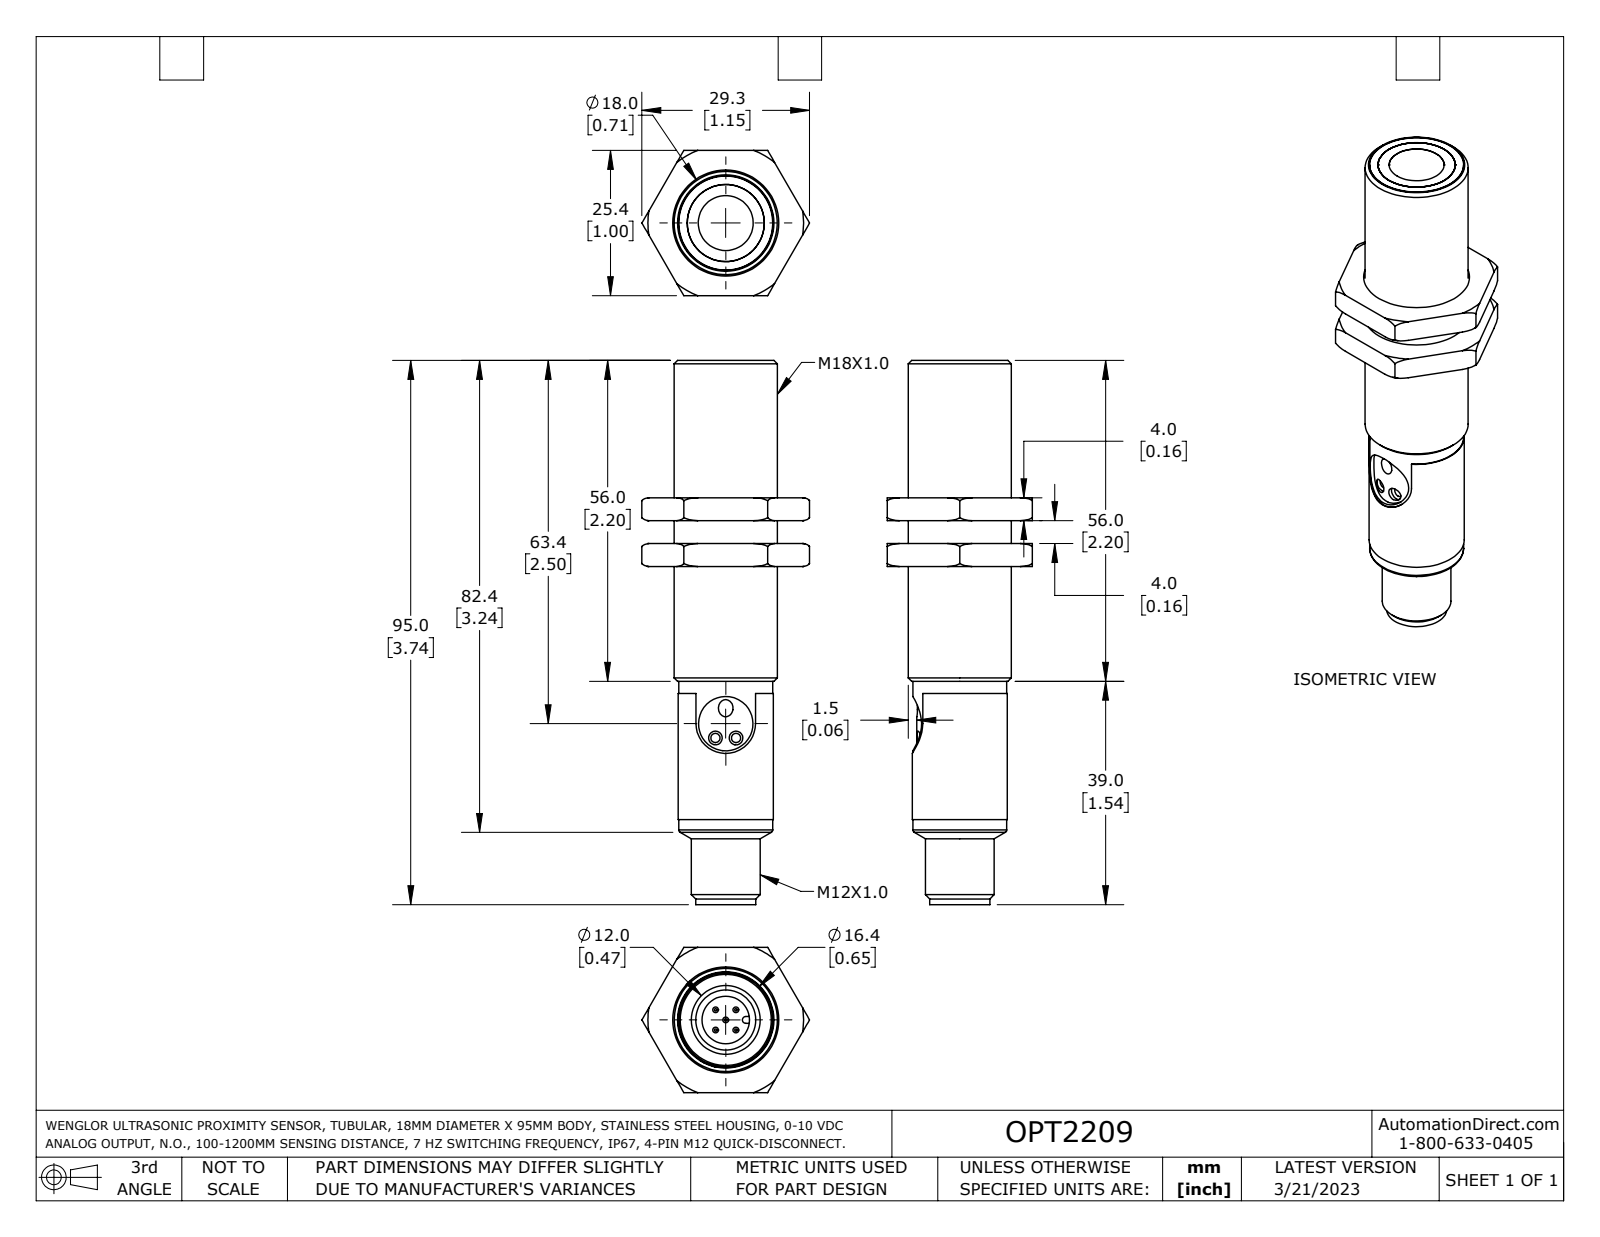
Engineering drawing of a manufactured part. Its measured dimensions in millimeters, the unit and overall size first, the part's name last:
Units: millimetres
Overall size (bounding box): 95 × 29.3 × 25.3
Round holes (diameter × count): ⌀2.4 ×2, ⌀3.8 ×1, ⌀4.5 ×1, ⌀8.3 ×1, ⌀9.5 ×1, ⌀9.6 ×1, ⌀13.5 ×1, ⌀17.5 ×1
Round bosses / shafts (diameter × count): ⌀1 ×5, ⌀18 ×1, ⌀16.6 ×1, ⌀16.4 ×1, ⌀12 ×1, ⌀10.5 ×1
Partial cylindrical surfaces — rounded edges, fillets, slot ends (radius × count): R0.5 ×4, R0.2 ×2, R1.3 ×2, R0.3 ×1, R0.6 ×1, R1.7 ×1, R5.2 ×1, R6.4 ×1
Main face-to-face distances: 4, 8, 25.3, 12, 36, 32, 28, 24, 50.1, 54.1
Hole centre spacings: 3.1, 5.5, 2.7, 3.6
Volume: 23 340 mm³ · Surface area: 8 387 mm²
Bodies: 3 solids, 137 faces (48 planar, 44 cylindrical, 45 other)
Part name (STEP PRODUCT): OPT2209
STEP written by: SolidWorks 2021 (AUTOMOTIVE_DESIGN)
